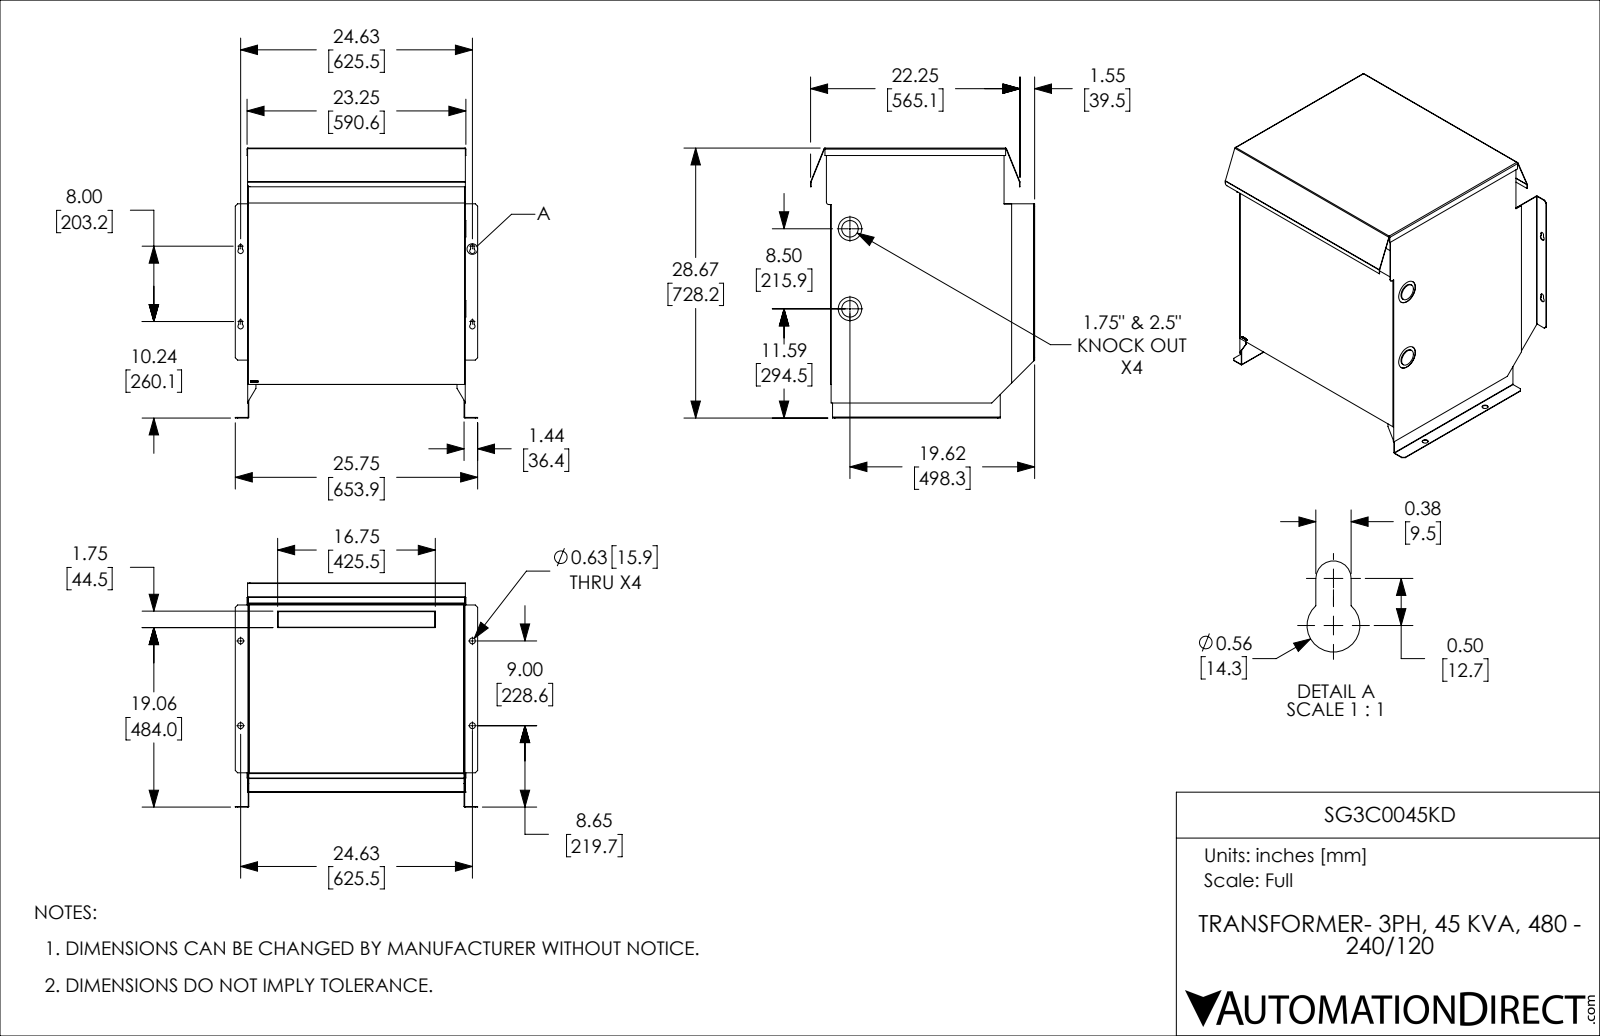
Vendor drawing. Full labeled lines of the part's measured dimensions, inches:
Part name (STEP PRODUCT): SG3C0045KD
STEP written by: SolidWorks 2018 (AUTOMOTIVE_DESIGN)
Units: inches
Bodies: 7 solids, 332 faces (217 planar, 81 cylindrical, 34 other)
Overall size (bounding box): 28.668 × 25.745 × 23.801
Volume: 205.5 in³ · Surface area: 7 302 in²
Round holes (diameter × count): ⌀0.625 ×4, ⌀2.5 ×2
Round bosses / shafts (diameter × count): ⌀1.75 ×2
Partial cylindrical surfaces — rounded edges, fillets, slot ends (radius × count): R0.03 ×12, R0.09 ×12, R0.06 ×6, R0.11 ×6, R0.188 ×4, R0.281 ×4, R0.25 ×3
Main face-to-face distances: 0.06, 0.05, 23.055, 22.995, 23.115, 17.996, 18.046, 18.056, 18.106, 25.058
Hole centre spacings: 9, 24.625, 26.218, 8.5
